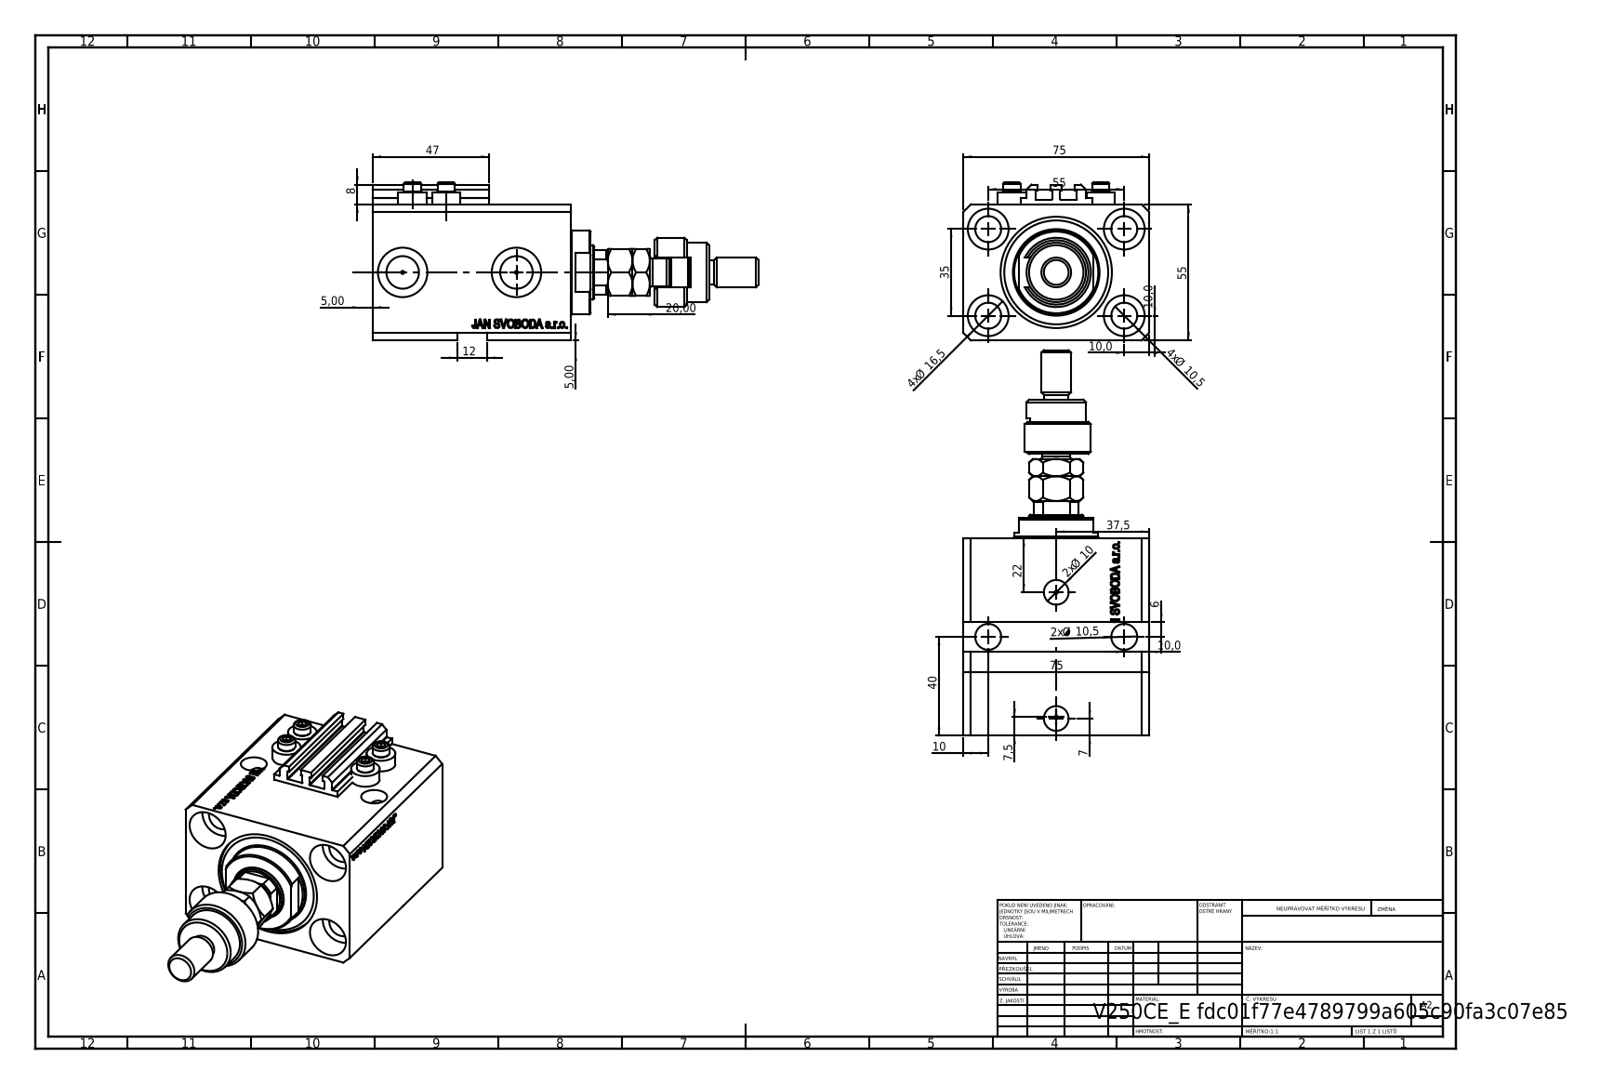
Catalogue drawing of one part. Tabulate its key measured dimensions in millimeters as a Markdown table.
| quantity | value |
| --- | --- |
| part name | V250CE_E_Body; V250CE_VC_E; FEMALE_PART_FOR_DFA; MFA (+2 more) |
| STEP written by | SolidWorks 2019 (CONFIG_CONTROL_DESIGN) |
| units | millimeters |
| bodies | 10 solids, 1149 faces (542 planar, 139 cylindrical, 468 other) |
| overall size | 155.9 × 75 × 64 |
| volume | 301 752 mm³ |
| surface area | 84 188 mm² |
| round holes (diameter × count) | 10.5 × 7, 1.25 × 4, 4 × 4, 16.5 × 4, 10 × 2, 13.16 × 2, 20 × 2, 22 × 1, 32 × 1, 45 × 1 |
| round bosses / shafts (diameter × count) | 11.6 × 4, 7 × 4, 34 × 1, 28 × 1, 24 × 1, 18 × 1, 12 × 1, 11 × 1 |
| partial cylindrical surfaces (radius × count) | 0.2 × 10, 9.75 × 1, 10.5 × 1 |
| main face-to-face distances | 55, 75, 27.1, 80, 3, 52.9, 9.9, 43, 70.1, 8 |
| hole center spacings | 32.6, 55, 13.6, 14.09, 19.89, 20.12, 25.81, 28.48 |
